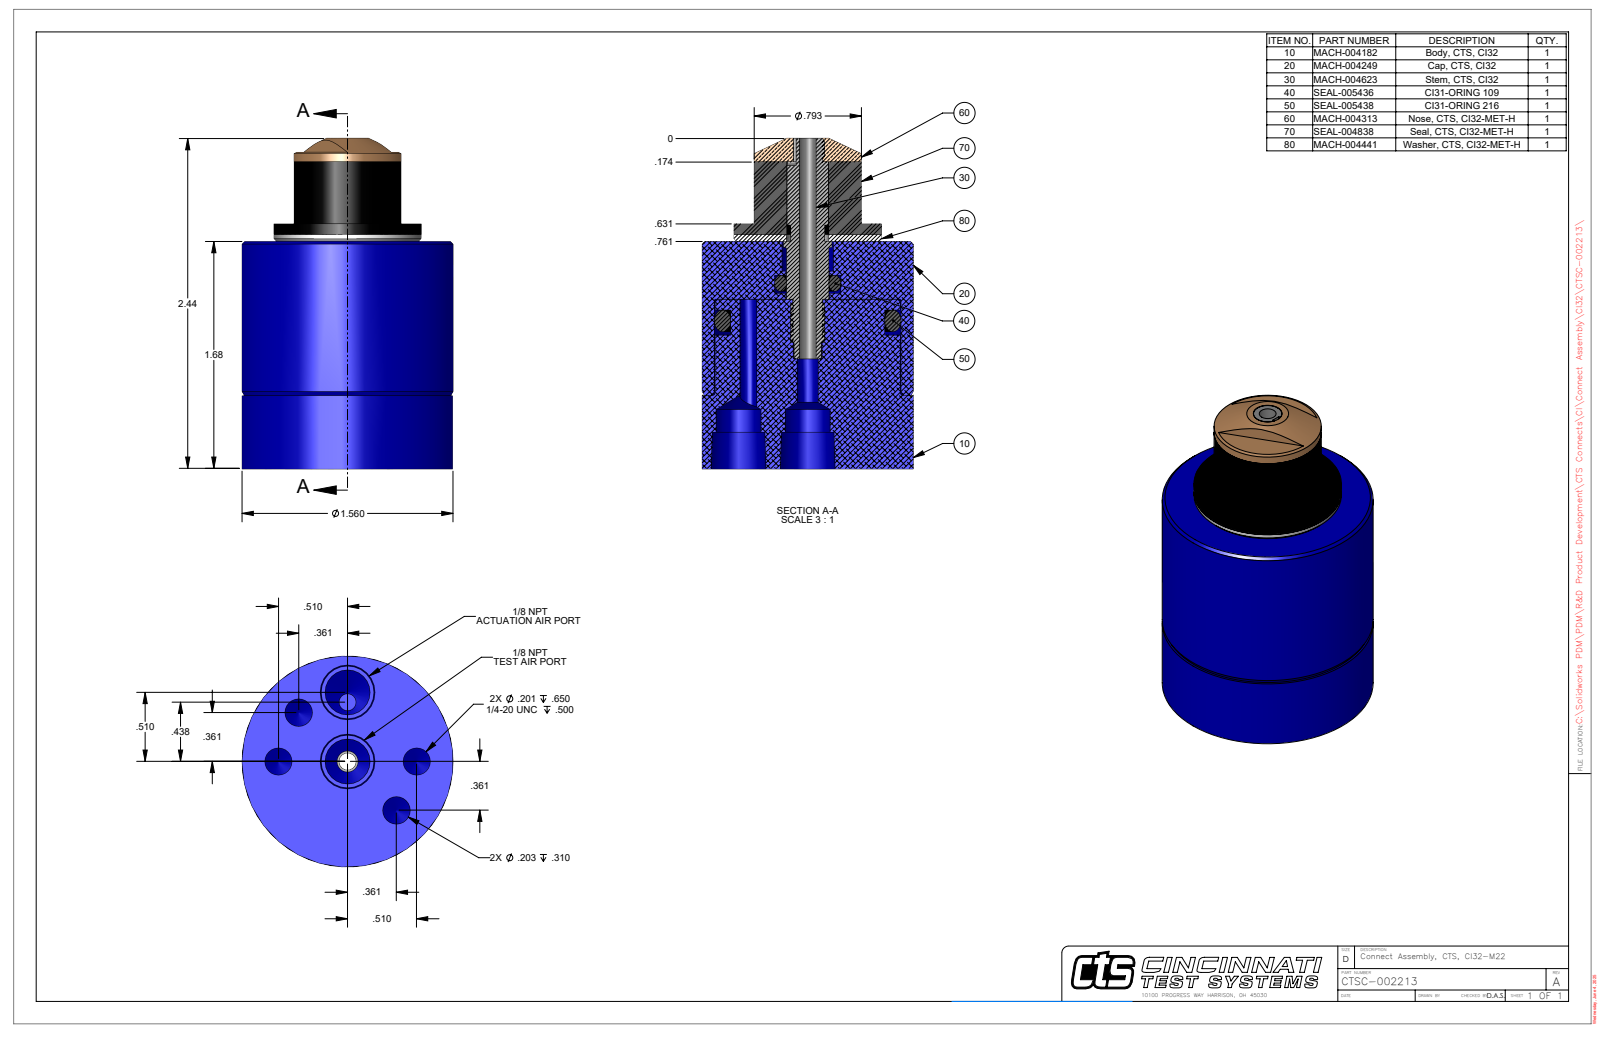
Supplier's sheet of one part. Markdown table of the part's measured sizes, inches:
| quantity | value |
| --- | --- |
| part name | CTSC-002213 |
| STEP written by | SolidWorks 2023 (AUTOMOTIVE_DESIGN) |
| units | inches |
| bodies | 1 solid, 103 faces (29 planar, 40 cylindrical, 34 other) |
| overall size | 2.438 × 1.56 × 1.56 |
| volume | 3.398 in³ |
| surface area | 19.8 in² |
| round holes (diameter × count) | 0.125 × 2, 0.201 × 2, 0.203 × 2, 0.332 × 2, 0.156 × 1, 0.213 × 1, 0.314 × 1, 0.38 × 1, 1.377 × 1 |
| round bosses / shafts (diameter × count) | 1.56 × 1, 1.365 × 1, 1.09 × 1, 0.793 × 1, 0.357 × 1, 0.31 × 1 |
| main face-to-face distances | 1.677, 1.807, 0.13, 2.334, 0.657, 0.527, 0.542, 1.135, 1.265, 1.792 |
| hole center spacings | 0.51, 0.39, 0.942, 0.672, 0.721, 0.072, 0.369, 0.437 |
